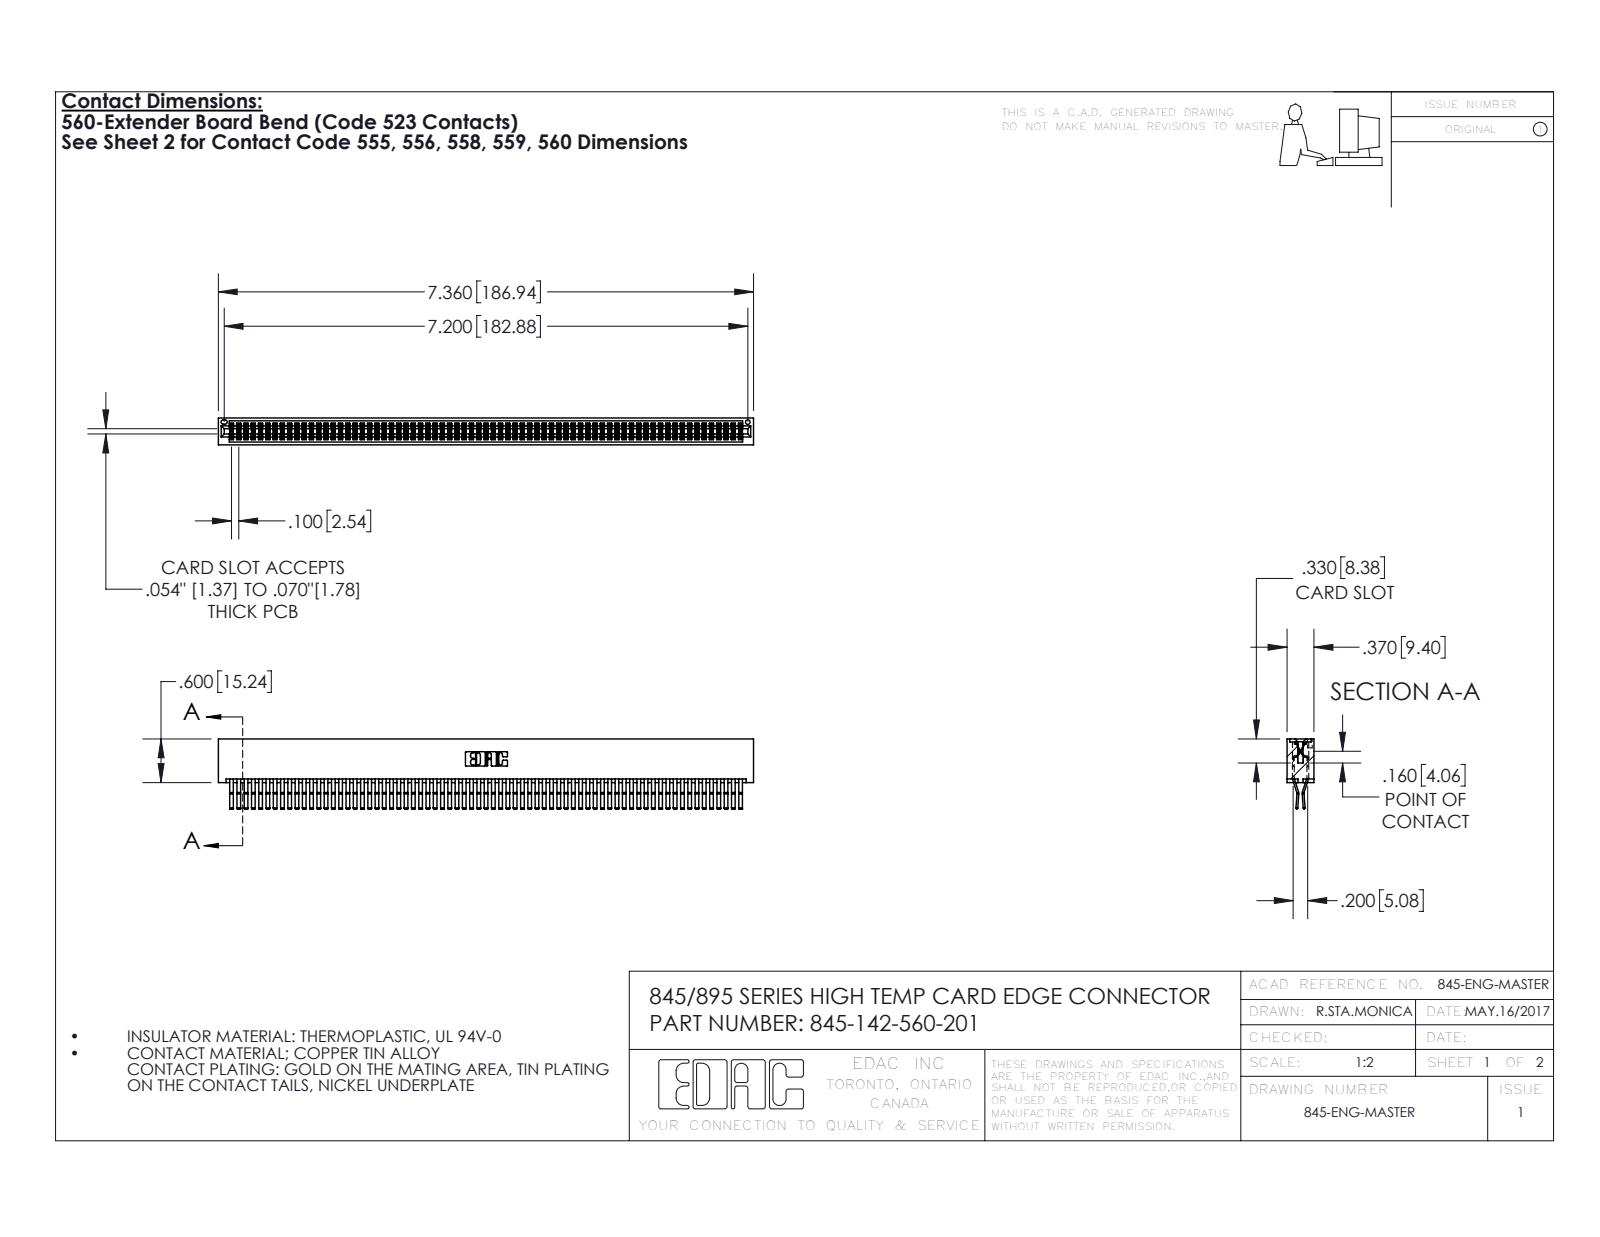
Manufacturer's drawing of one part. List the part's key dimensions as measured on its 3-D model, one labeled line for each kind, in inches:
Part name (STEP PRODUCT): 345 Part_No Mounting Lugs; 345-292-001_560 Tail; 345-142-560-201
STEP written by: SolidWorks 2016 (CONFIG_CONTROL_DESIGN)
Units: inches
Bodies: 143 solids, 7502 faces (4762 planar, 2740 cylindrical, 0 other)
Overall size (bounding box): 7.36 × 0.962 × 0.37
Volume: 1.219 in³ · Surface area: 50.82 in²
Round holes (diameter × count): ⌀0.064 ×1
Partial cylindrical surfaces — rounded edges, fillets, slot ends (radius × count): R0.006 ×213, R0.01 ×22, R0.007 ×6, R0.031 ×6, R0.026 ×3, R0.01 ×2, R0.014 ×2, R0.019 ×2
Main face-to-face distances: 0.025, 0.298, 0.072, 0.37, 0.2, 0.098, 0.272, 0.225, 0.175, 0.149
